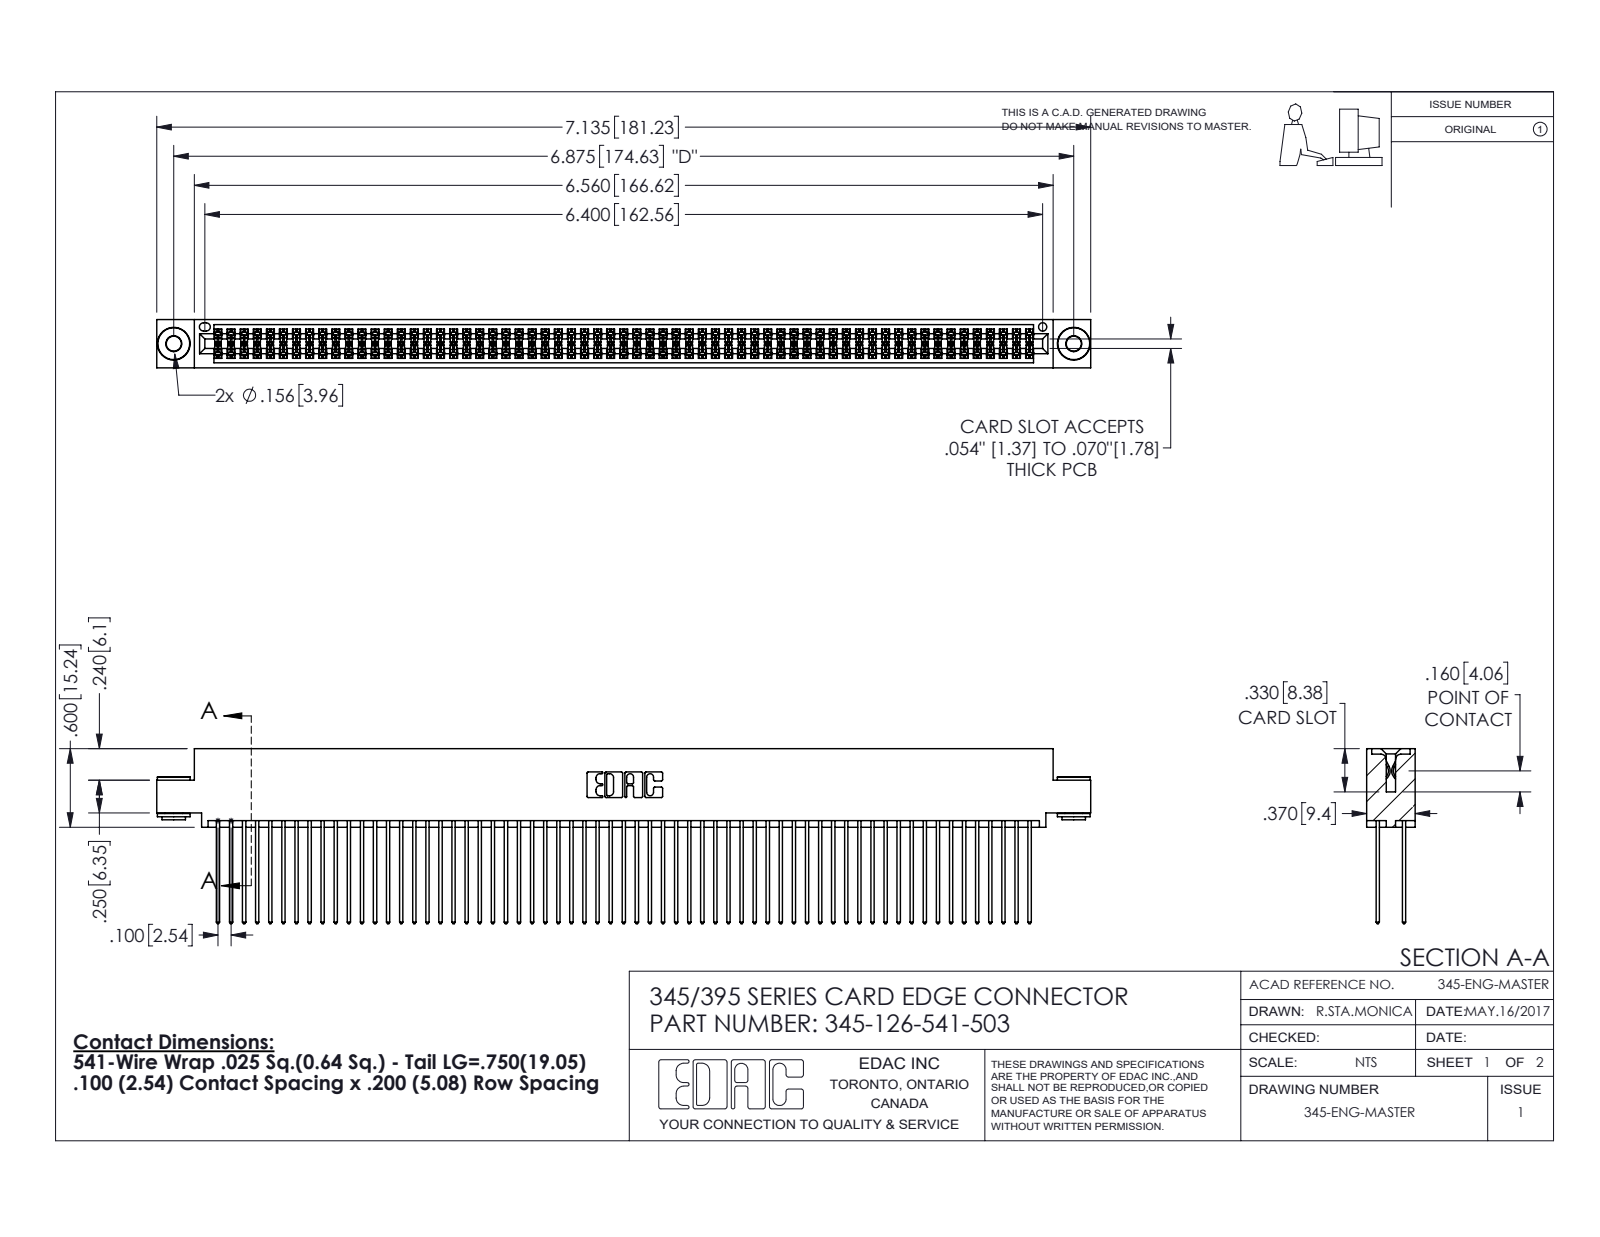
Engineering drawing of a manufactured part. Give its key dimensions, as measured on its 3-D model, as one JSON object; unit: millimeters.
{"part_name": "345 Part_0.110 Offset - 0.156 Dia-TH; 345-126-541-503; 345-292-001_345-293-141; 345-250-002_345-250-002-102", "step_written_by": "SolidWorks 2016 (CONFIG_CONTROL_DESIGN)", "units": "millimeters", "bodies": {"solids": 129, "faces": 6468, "planar": 4252, "cylindrical": 2208, "other": 8}, "overall_size": [181.2, 34, 9.4], "volume_mm3": 18470, "surface_area_mm2": 31400, "round_holes": [[2.9, 2], [4, 2], [1.6, 1]], "round_bosses_or_shafts": [[6.4, 2], [4.6, 2], [3.5, 2]], "partial_cylinders_radius": [[0.2, 189], [0.3, 126], [0.3, 22], [0.2, 6], [0.8, 6], [0.7, 3], [0.4, 2], [0.5, 2]], "face_to_face_distances": [1.8, 7.6, 5.1, 0.6, 2.5, 6.9, 5.7, 9.4, 4.4, 3.8], "hole_center_spacings": [6.9, 168.6, 174.6]}
